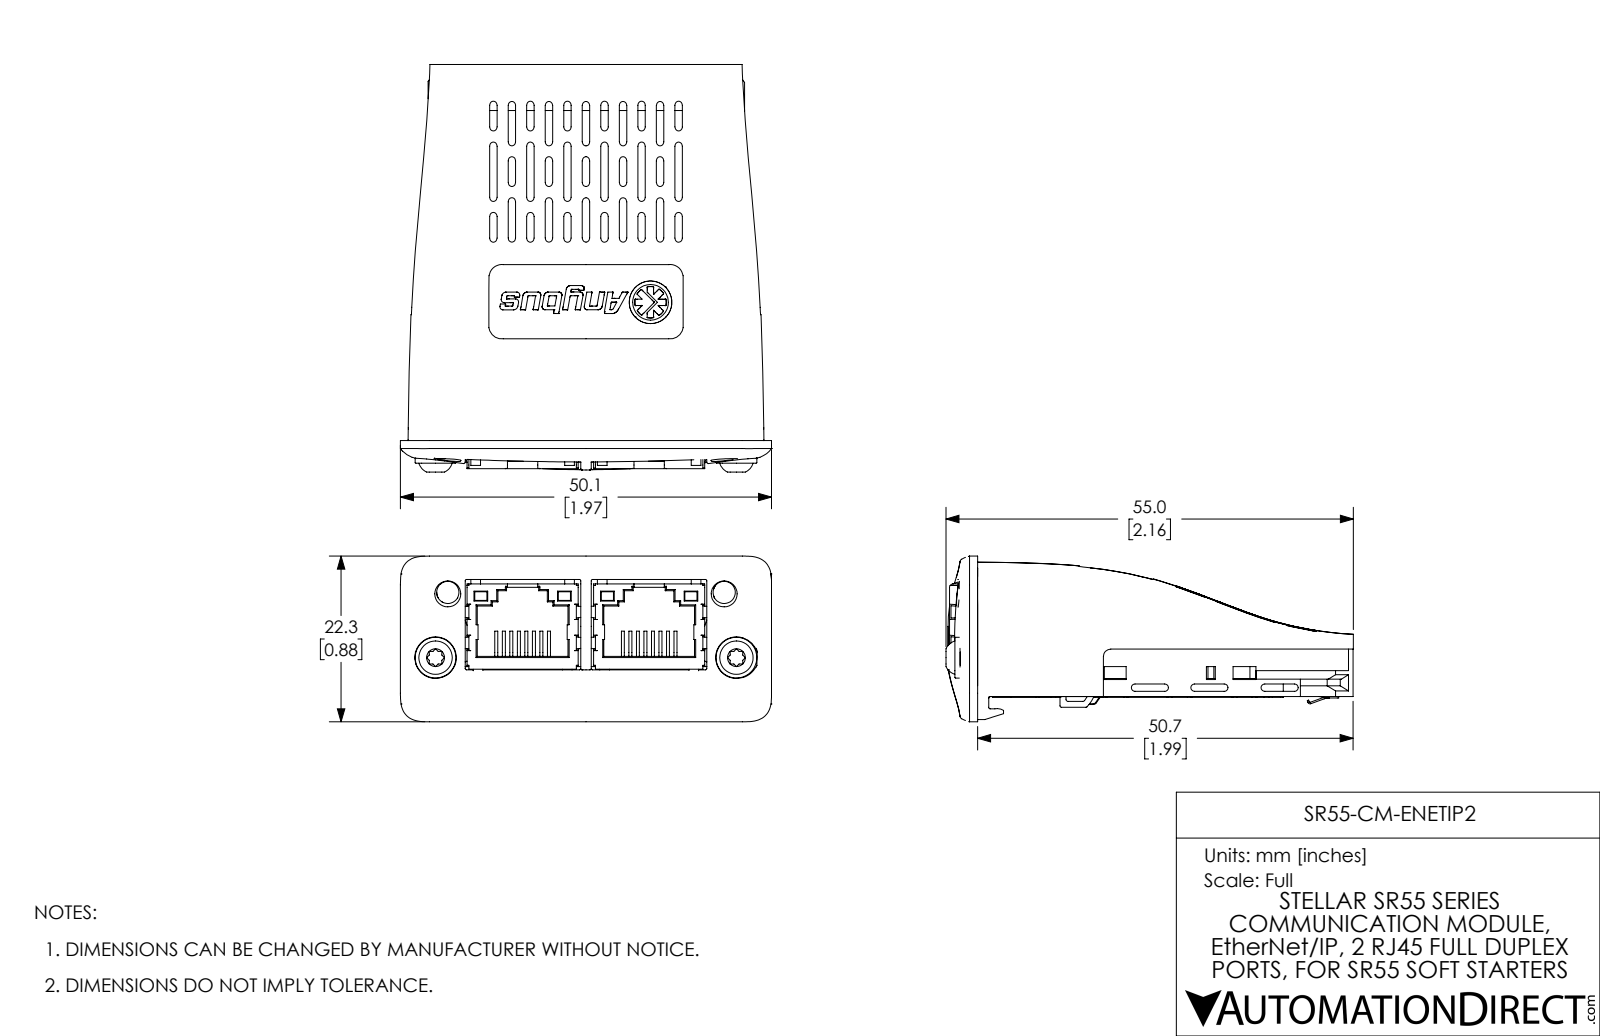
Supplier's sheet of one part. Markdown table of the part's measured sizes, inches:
| quantity | value |
| --- | --- |
| part name | ABCC 2xRJ45 with housing r1 1Dr1 ext1 R1 |
| STEP written by | SolidWorks 2017 (AUTOMOTIVE_DESIGN) |
| units | inches |
| bodies | 16 solids, 3902 faces (2597 planar, 950 cylindrical, 355 other) |
| overall size | 2.171 × 1.972 × 0.897 |
| volume | 0.794 in³ |
| surface area | 46.91 in² |
| round holes (diameter × count) | 0.039 × 50, 0.024 × 8, 0.039 × 2, 0.091 × 2, 0.106 × 2, 0.11 × 2, 0.138 × 2, 0.22 × 1 |
| round bosses / shafts (diameter × count) | 0.079 × 6, 0.087 × 4, 0.217 × 2, 0.157 × 2, 0.118 × 2, 0.098 × 2, 0.189 × 1, 0.059 × 1 |
| partial cylindrical surfaces (radius × count) | 0.008 × 135, 0.004 × 57, 0.01 × 41, 0.012 × 37, 0.02 × 37, 0.016 × 29, 0.006 × 12, 0.039 × 6 |
| main face-to-face distances | 0.156, 0.093, 0.063, 0.089, 0.152, 0.1, 0.163, 0.138, 0.591, 0.142 |
| hole center spacings | 0.05, 0.1, 0.071, 0.15, 0.112, 0.2, 0.158, 0.206 |
